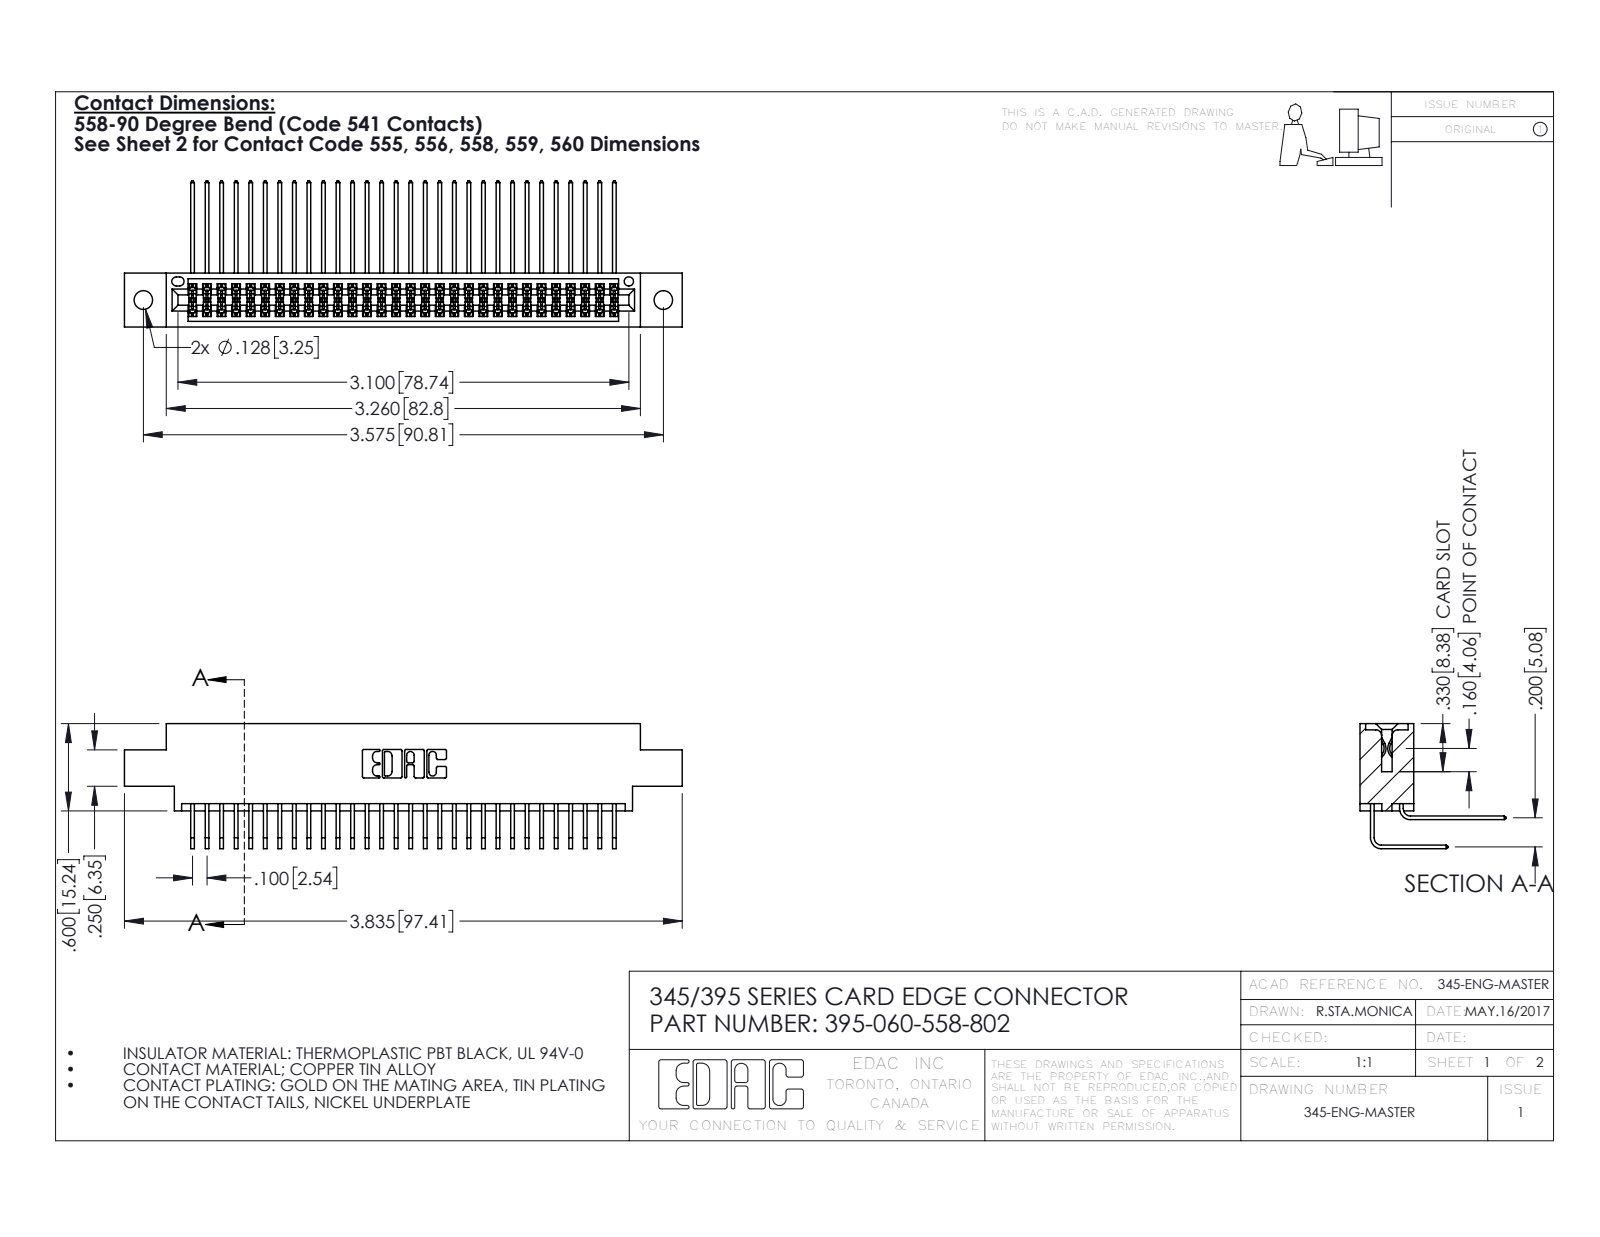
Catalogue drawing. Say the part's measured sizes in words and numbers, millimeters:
The part is named "345 Part_0.170 Offset - 0.128 Dia; 345-292-001_558 559 Tail - 1; 395-060-558-802; 345-292-001_558 Tail - 2". Its 3-D file was written by "SolidWorks 2016 (CONFIG_CONTROL_DESIGN)". It is 61 solids with 3250 faces: 2184 planar, 1066 cylindrical and 0 other. Overall it measures 97.4 by 25.5 by 21.8 millimeters. Its volume is 9 550 cubic millimeters and its surface area 15 380 square millimeters. Round holes: 2 of diameter 3.3, 1 of diameter 1.6. Partial cylindrical surfaces (rounded edges, fillets, slot ends): 91 of radius 0.2, 22 of radius 0.3, 6 of radius 0.2, 6 of radius 0.8, 3 of radius 0.7, 2 of radius 0.4, 2 of radius 0.5, 2 of radius 0.6. The main face-to-face distances are 1.8, 7.6, 5.1, 9.4, 2.5, 6.9, 0.6, 5.7, 4.4, 0.6. The hole center spacings are 6.9, 84.8, 90.8.
